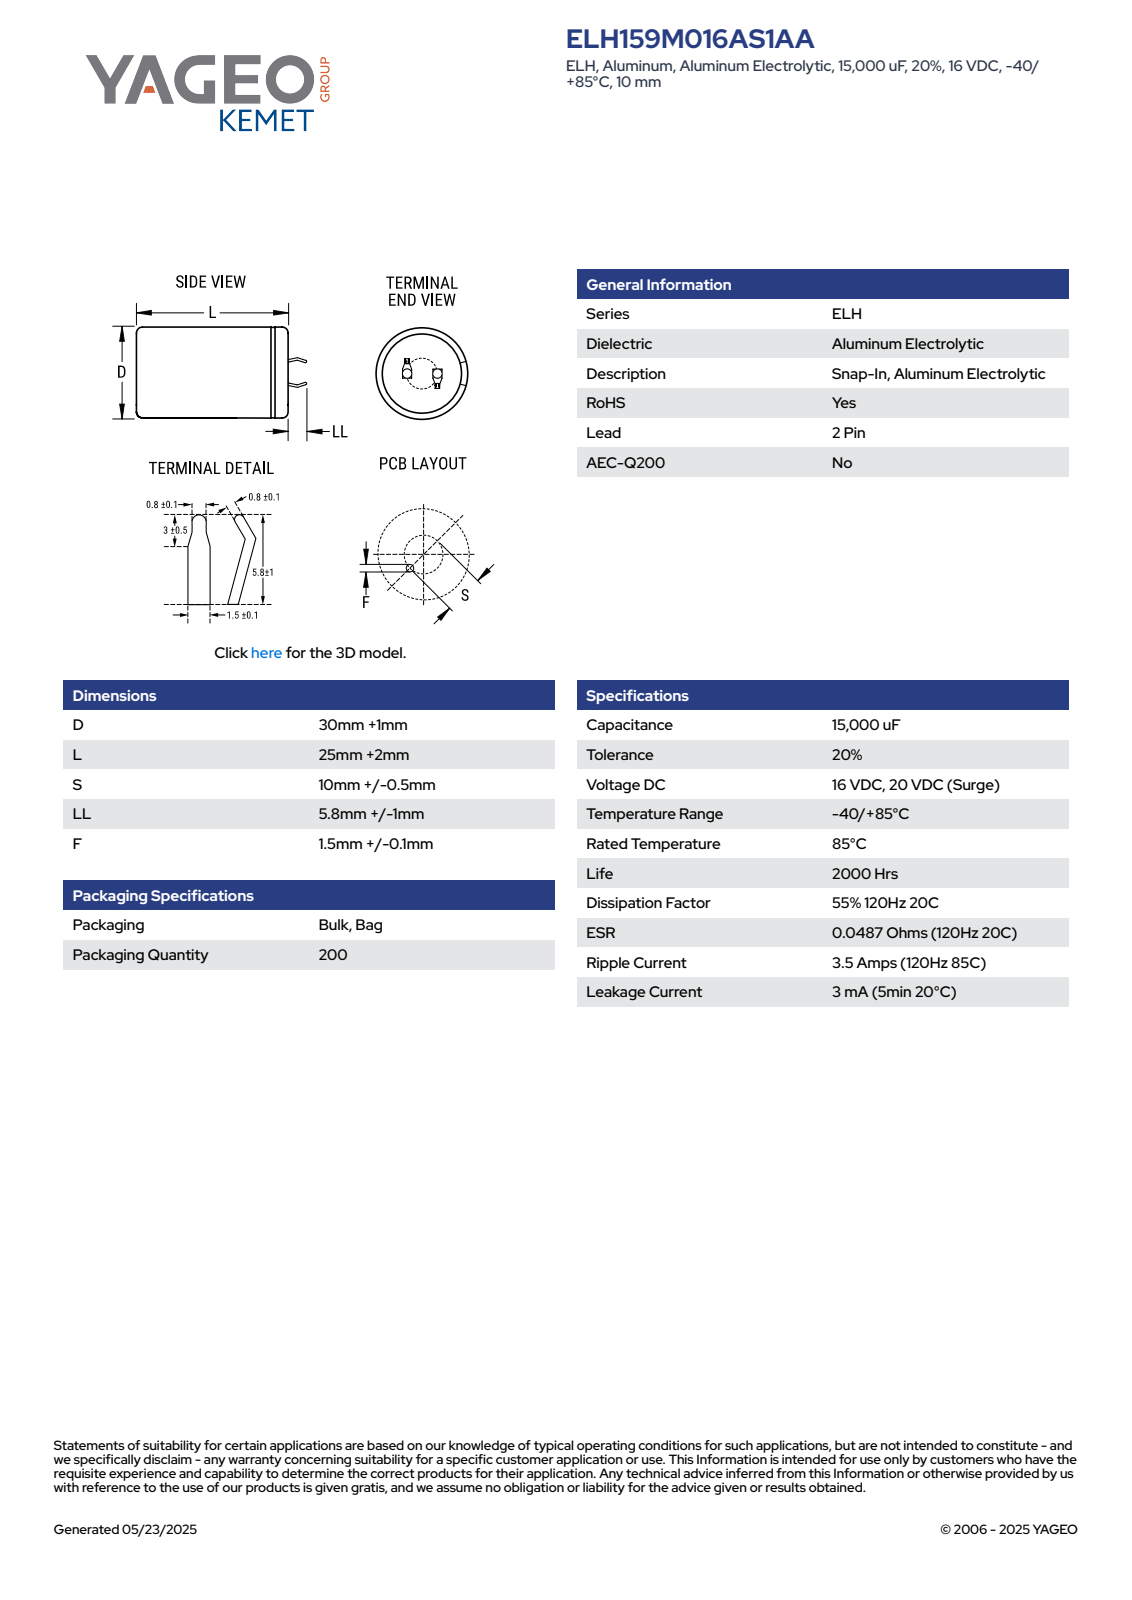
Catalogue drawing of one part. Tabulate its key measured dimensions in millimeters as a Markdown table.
| quantity | value |
| --- | --- |
| part name | CARS_K2P_30X25_D31L27S10LL6.8F1.6 |
| STEP written by | SolidWorks 2014 (AUTOMOTIVE_DESIGN) |
| units | millimeters |
| bodies | 1 solid, 100 faces (52 planar, 9 cylindrical, 39 other) |
| overall size | 33.79 × 31 × 31 |
| volume | 20 045 mm³ |
| surface area | 4 147 mm² |
| round holes (diameter × count) | 27.43 × 1 |
| round bosses / shafts (diameter × count) | 31 × 1 |
| partial cylindrical surfaces (radius × count) | 15.49 × 1 |
| main face-to-face distances | 26.99, 27.49, 0.5, 0.6, 7.08, 0.75, 1.35, 7.68, 6.48, 0.59 |
